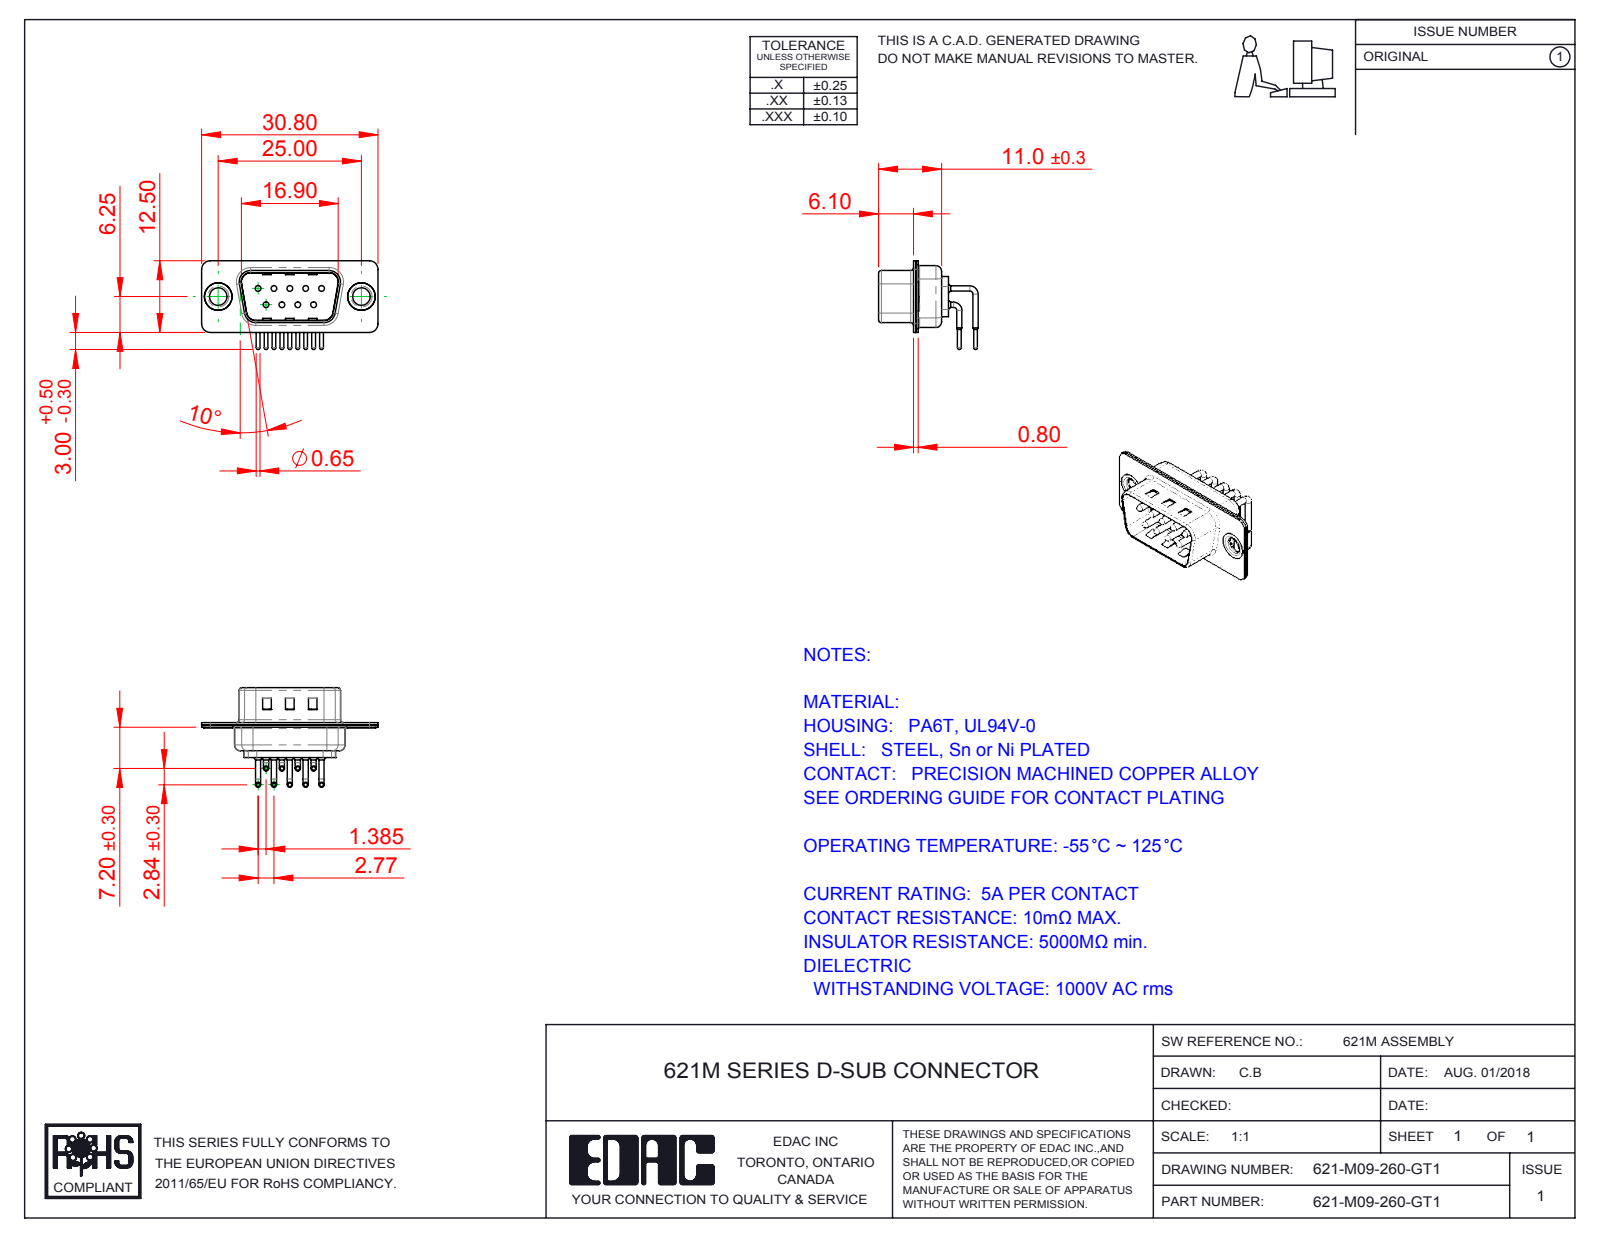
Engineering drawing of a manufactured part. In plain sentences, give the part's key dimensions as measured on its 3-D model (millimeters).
The part is named "621M Contact Row 2; 621M Housing_09 Contacts; 621M Shell Front_09 Contacts; 621M Contact Row 1 (+3 more)". Its 3-D file was written by "SolidWorks 2016 (CONFIG_CONTROL_DESIGN)". It is 14 solids with 1268 faces: 683 planar, 437 cylindrical and 148 other. Overall it measures 30.8 by 17.39 by 15.49 millimeters. Its volume is 1 289 cubic millimeters and its surface area 3 701 square millimeters. Round holes: 9 of diameter 1, 9 of diameter 1.7, 9 of diameter 2, 2 of diameter 3.05, 2 of diameter 4, 2 of diameter 4.8. Round bosses or shafts: 18 of diameter 0.9, 9 of diameter 1.5, 9 of diameter 0.65, 2 of diameter 5, 2 of diameter 4.9, 2 of diameter 3.55. Partial cylindrical surfaces (rounded edges, fillets, slot ends): 16 of radius 1.5, 12 of radius 2, 9 of radius 1.01, 8 of radius 0.5, 8 of radius 1.6, 4 of radius 0.25, 4 of radius 0.6, 4 of radius 0.65. The main face-to-face distances are 0.4, 0.85, 0.8, 9.55, 1.25, 10.4, 8.7, 0.35, 6.1, 5.7. The hole center spacings are 3.16, 2.77, 5.54, 5.03, 5.04, 8.31, 7.1, 7.48.
